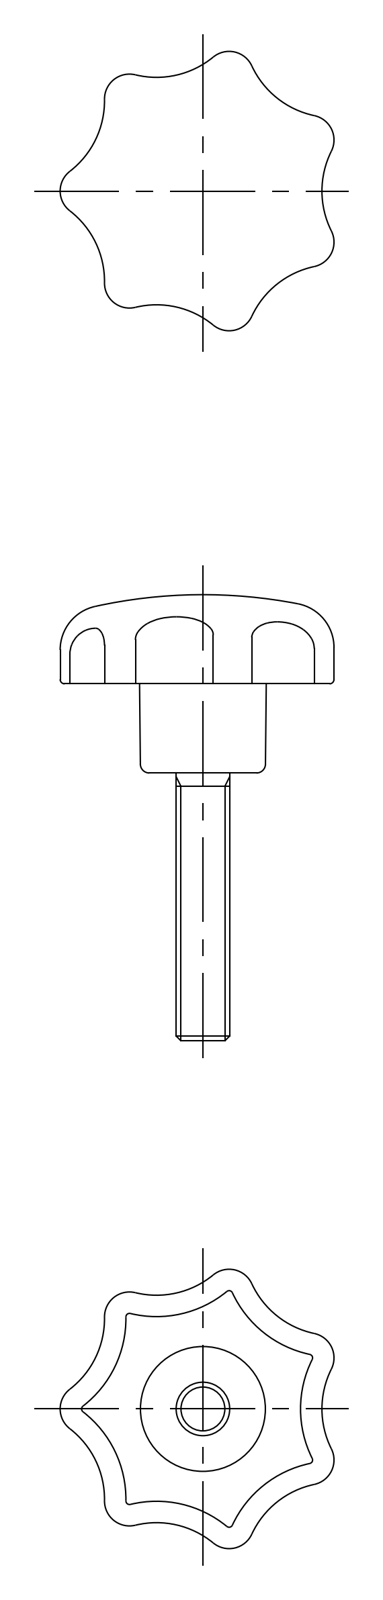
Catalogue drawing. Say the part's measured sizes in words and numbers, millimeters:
The part is named "screw; knob; KSM_32_M6_30_24618_36". Its 3-D file was written by "CADfix (AUTOMOTIVE_DESIGN)". It is 2 solids with 106 faces: 0 planar, 0 cylindrical and 106 other. Overall it measures 50 by 31.34 by 30.69 millimeters. Its volume is 6 248 cubic millimeters and its surface area 4 487 square millimeters.
